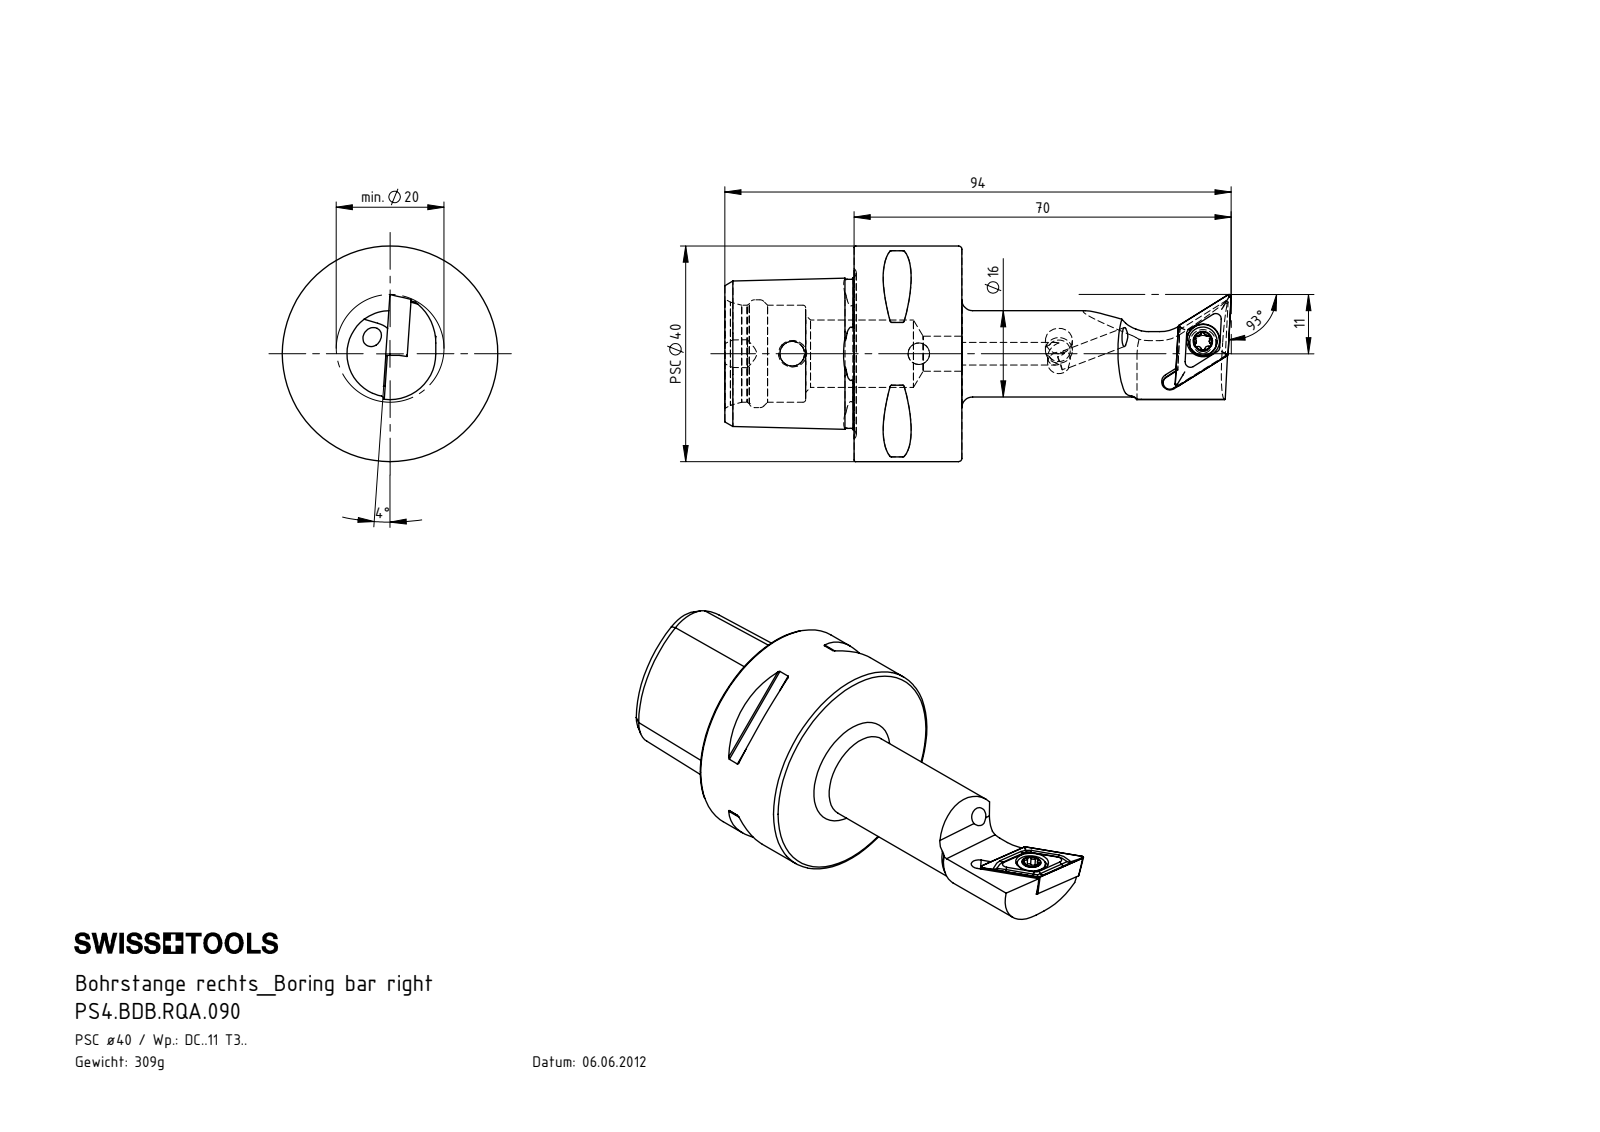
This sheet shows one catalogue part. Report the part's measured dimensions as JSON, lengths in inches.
{"part_name": "KVT_MB_600_050; DCMT11T304; PS4-BDB.RQA.090_A; PS4.BDB.RQA.090 (+1 more)", "step_written_by": "SolidWorks 2017 (AUTOMOTIVE_DESIGN)", "units": "inches", "bodies": {"solids": 5, "faces": 292, "planar": 53, "cylindrical": 73, "other": 166}, "overall_size": [4.488, 1.575, 1.575], "volume_in3": 3.491, "surface_area_in2": 24.28, "round_holes": [[0.157, 2], [0.165, 2], [0.13, 1], [0.173, 1], [0.181, 1], [0.197, 1], [0.24, 1], [0.256, 1], [0.492, 1], [0.709, 1], [0.787, 1]], "round_bosses_or_shafts": [[1.575, 1], [0.984, 1], [0.207, 1], [0.197, 1], [0.157, 1]], "partial_cylinders_radius": [[0.012, 8], [0.013, 6], [0.023, 6], [0.118, 2], [0.049, 1], [0.512, 1], [0.591, 1], [1.024, 1]], "face_to_face_distances": [0.787, 0.945, 1.732, 0.144, 0.611, 1.39, 0.591, 0.354, 1.142, 0.937], "hole_center_spacings": [0.925]}
